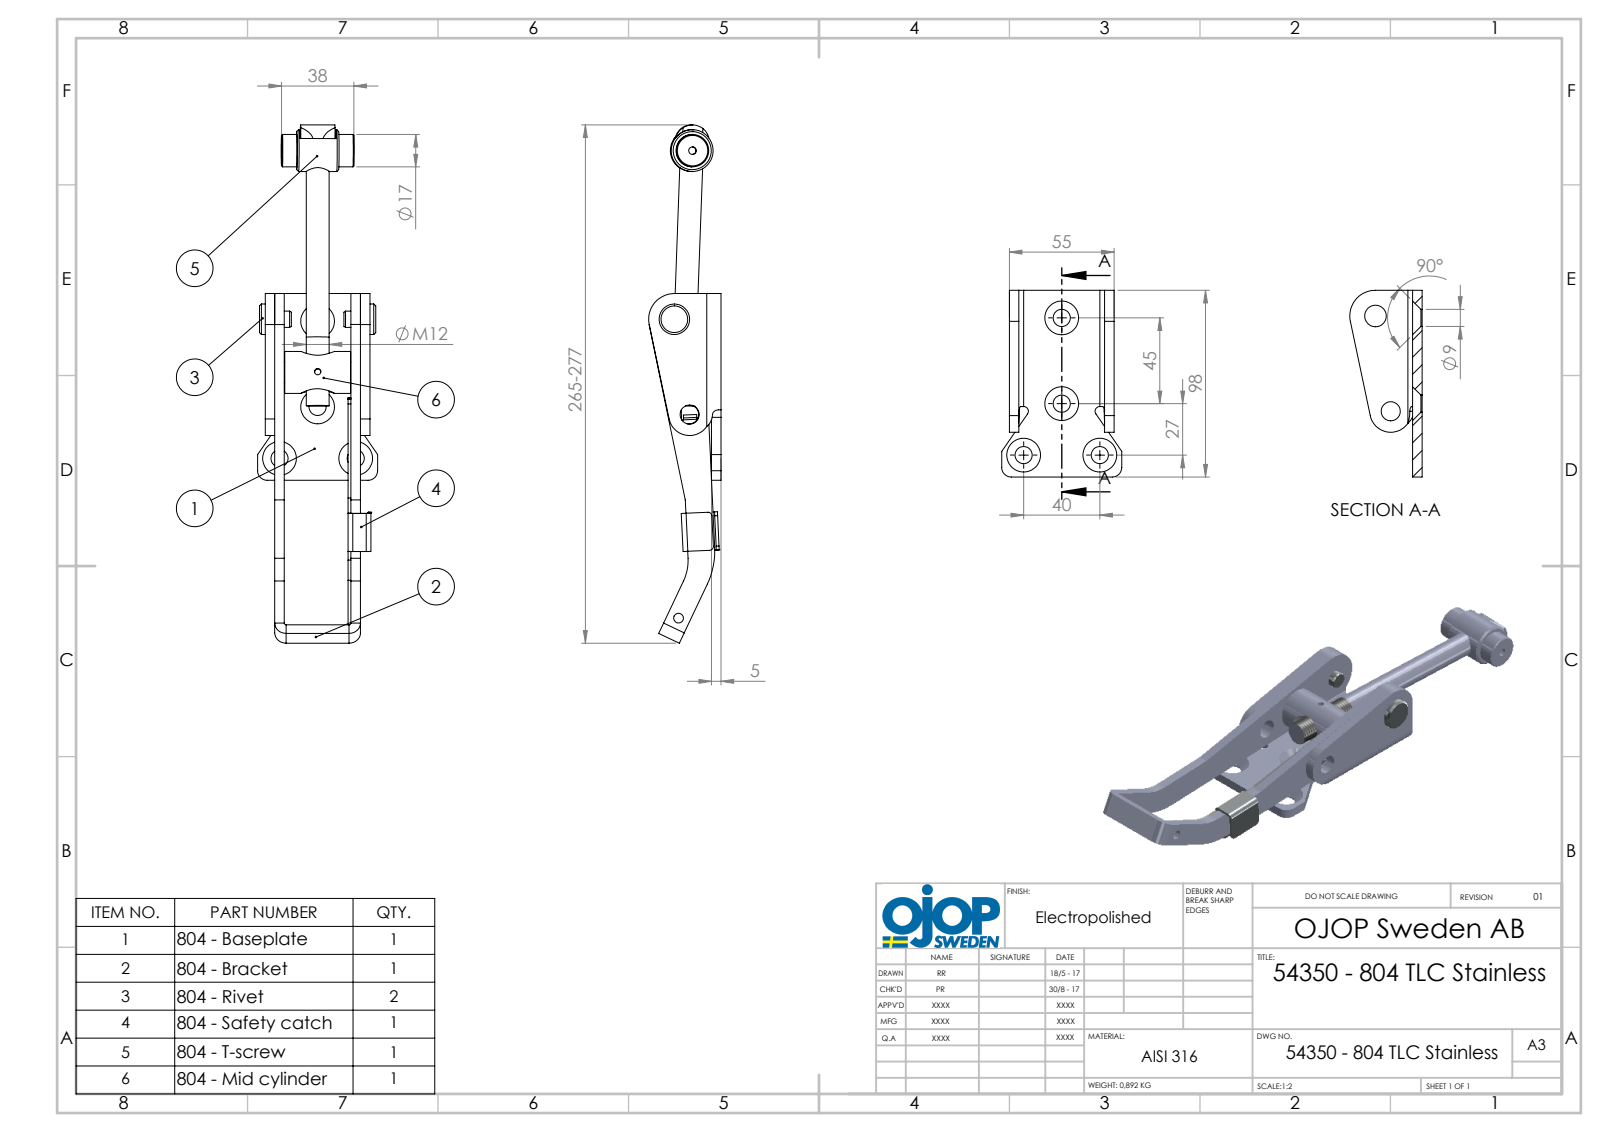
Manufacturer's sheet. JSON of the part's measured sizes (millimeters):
{"part_name": "Platta 804; 804 Bygel; 804 - spärr; T-skruv 804 (+5 more)", "step_written_by": "SolidWorks 2015 (AUTOMOTIVE_DESIGN)", "units": "millimeters", "bodies": {"solids": 8, "faces": 255, "planar": 112, "cylindrical": 109, "other": 34}, "overall_size": [271.92, 63, 35.5], "volume_mm3": 115669, "surface_area_mm2": 58596, "round_holes": [[9, 4], [10, 2], [3.3, 1], [4, 1], [5.1, 1], [8.6, 1], [11.2, 1], [11.3, 1], [12, 1], [12.3, 1]], "round_bosses_or_shafts": [[22, 2], [17, 1], [16, 1], [12.01, 1], [12, 1], [11, 1], [10.9, 1], [8.5, 1]], "partial_cylinders_radius": [[2.5, 8], [1, 6], [2, 6], [5, 2], [6, 2], [7.5, 2], [25, 2], [40, 2]], "face_to_face_distances": [5, 45, 40, 10, 50, 35, 1.5, 38.5, 33.5, 6.5], "hole_center_spacings": [33.6, 74.73, 1.7, 22.22, 22.31, 28.33, 40, 45]}
